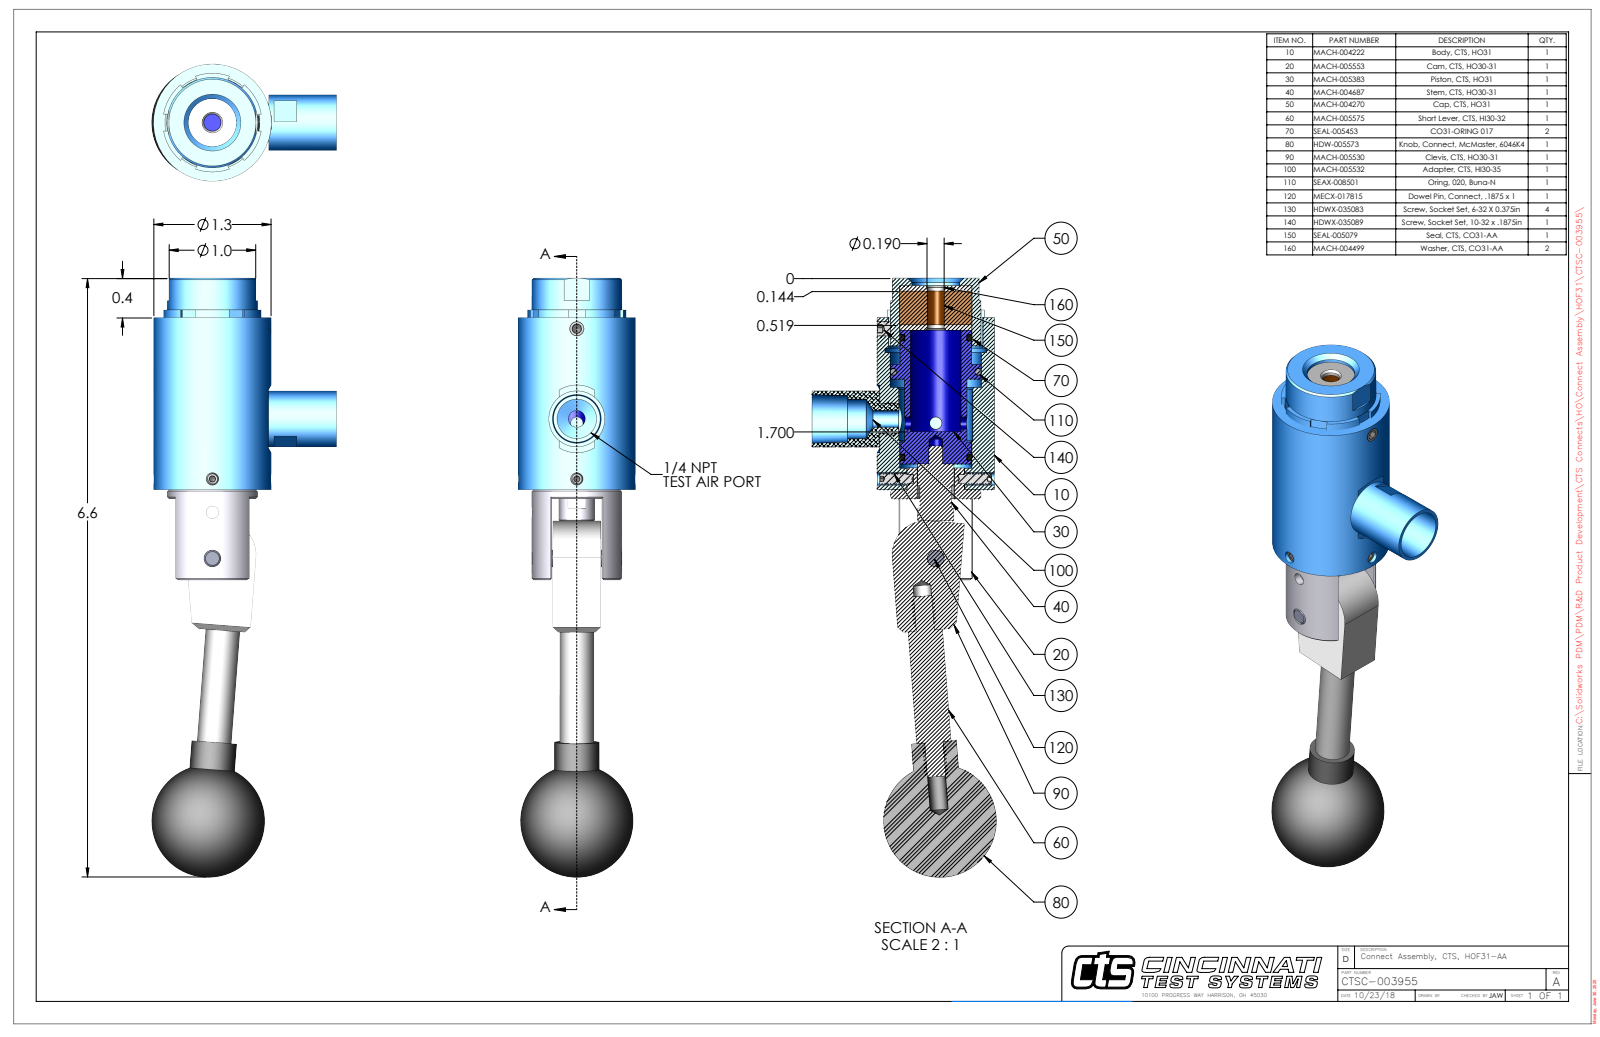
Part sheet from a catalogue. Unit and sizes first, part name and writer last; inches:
Units: inches
Overall size (bounding box): 6.636 × 2.042 × 1.3
Round holes (diameter × count): ⌀0.136 ×2, ⌀0.19 ×2, ⌀0.201 ×2, ⌀0.138 ×1, ⌀0.15 ×1, ⌀0.159 ×1, ⌀0.187 ×1, ⌀0.189 ×1, ⌀0.192 ×1, ⌀0.332 ×1, ⌀0.418 ×1, ⌀0.438 ×1
Round bosses / shafts (diameter × count): ⌀0.138 ×2, ⌀1.3 ×1, ⌀1 ×1, ⌀0.792 ×1, ⌀0.79 ×1, ⌀0.69 ×1, ⌀0.63 ×1, ⌀0.62 ×1
Partial cylindrical surfaces — rounded edges, fillets, slot ends (radius × count): R0.374 ×1, R0.375 ×1, R0.524 ×1, R0.547 ×1
Main face-to-face distances: 0.059, 0.434, 0.012, 0.542, 0.375, 0.53, 0.554, 0.493, 1.766, 1.825
Hole centre spacings: 0.047, 0.51, 0.987, 0.997, 1.044, 1.497
Volume: 4.563 in³ · Surface area: 46.84 in²
Bodies: 14 solids, 532 faces (173 planar, 217 cylindrical, 142 other)
Part name (STEP PRODUCT): CTSC-003955
STEP written by: SolidWorks 2023 (AUTOMOTIVE_DESIGN)
